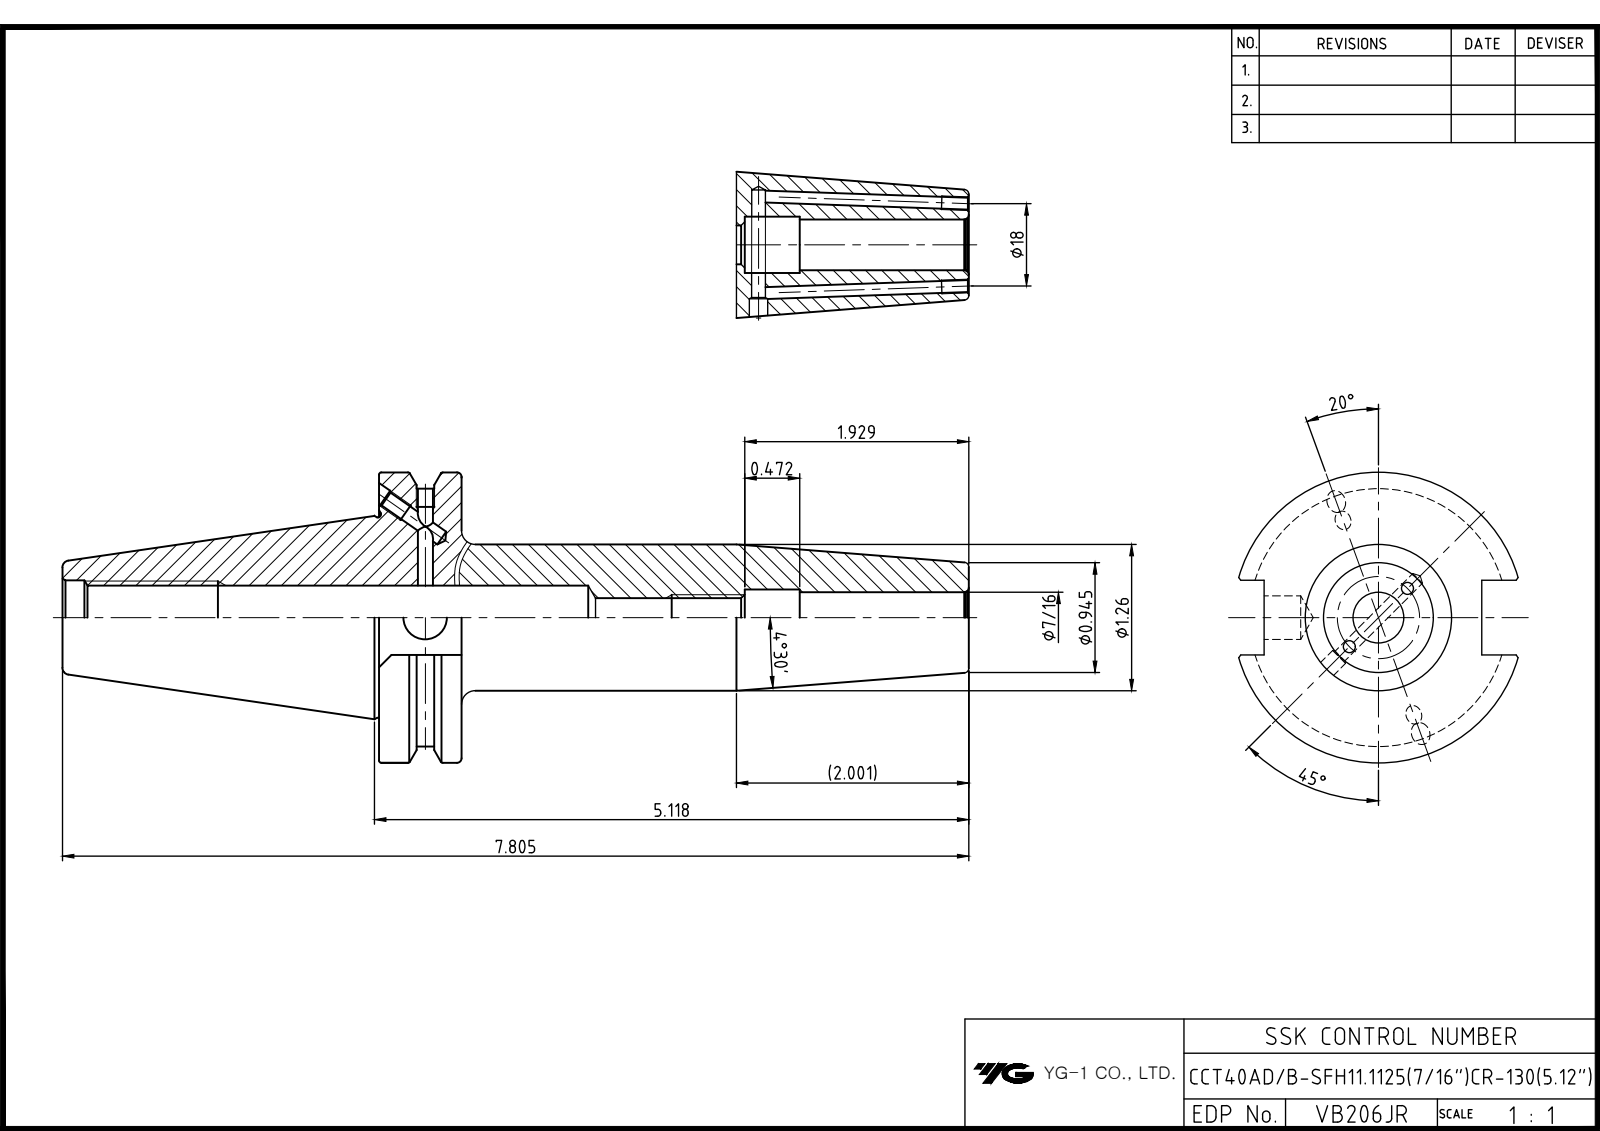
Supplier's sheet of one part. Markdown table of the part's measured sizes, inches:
| quantity | value |
| --- | --- |
| part name | LO-CCT40ADB-SFH11.1125CR-130 |
| STEP written by | Autodesk Inventor 2026 (AUTOMOTIVE_DESIGN) |
| units | inches |
| bodies | 1 solid, 88 faces (37 planar, 29 cylindrical, 22 other) |
| overall size | 7.805 × 2.5 × 2.405 |
| volume | 10.5 in³ |
| surface area | 55.26 in² |
| round holes (diameter × count) | 0.128 × 4, 0.097 × 2, 0.157 × 2, 0.165 × 2, 0.351 × 1, 0.375 × 1, 0.437 × 1, 0.484 × 1, 0.527 × 1, 0.642 × 1 |
| round bosses / shafts (diameter × count) | 2.5 × 1, 1.26 × 1 |
| partial cylindrical surfaces (radius × count) | 1.108 × 1 |
| main face-to-face distances | 0.711, 5.079, 4.368, 1.874, 0.645, 2.726, 3.437, 7.805, 3.201, 0.474 |
